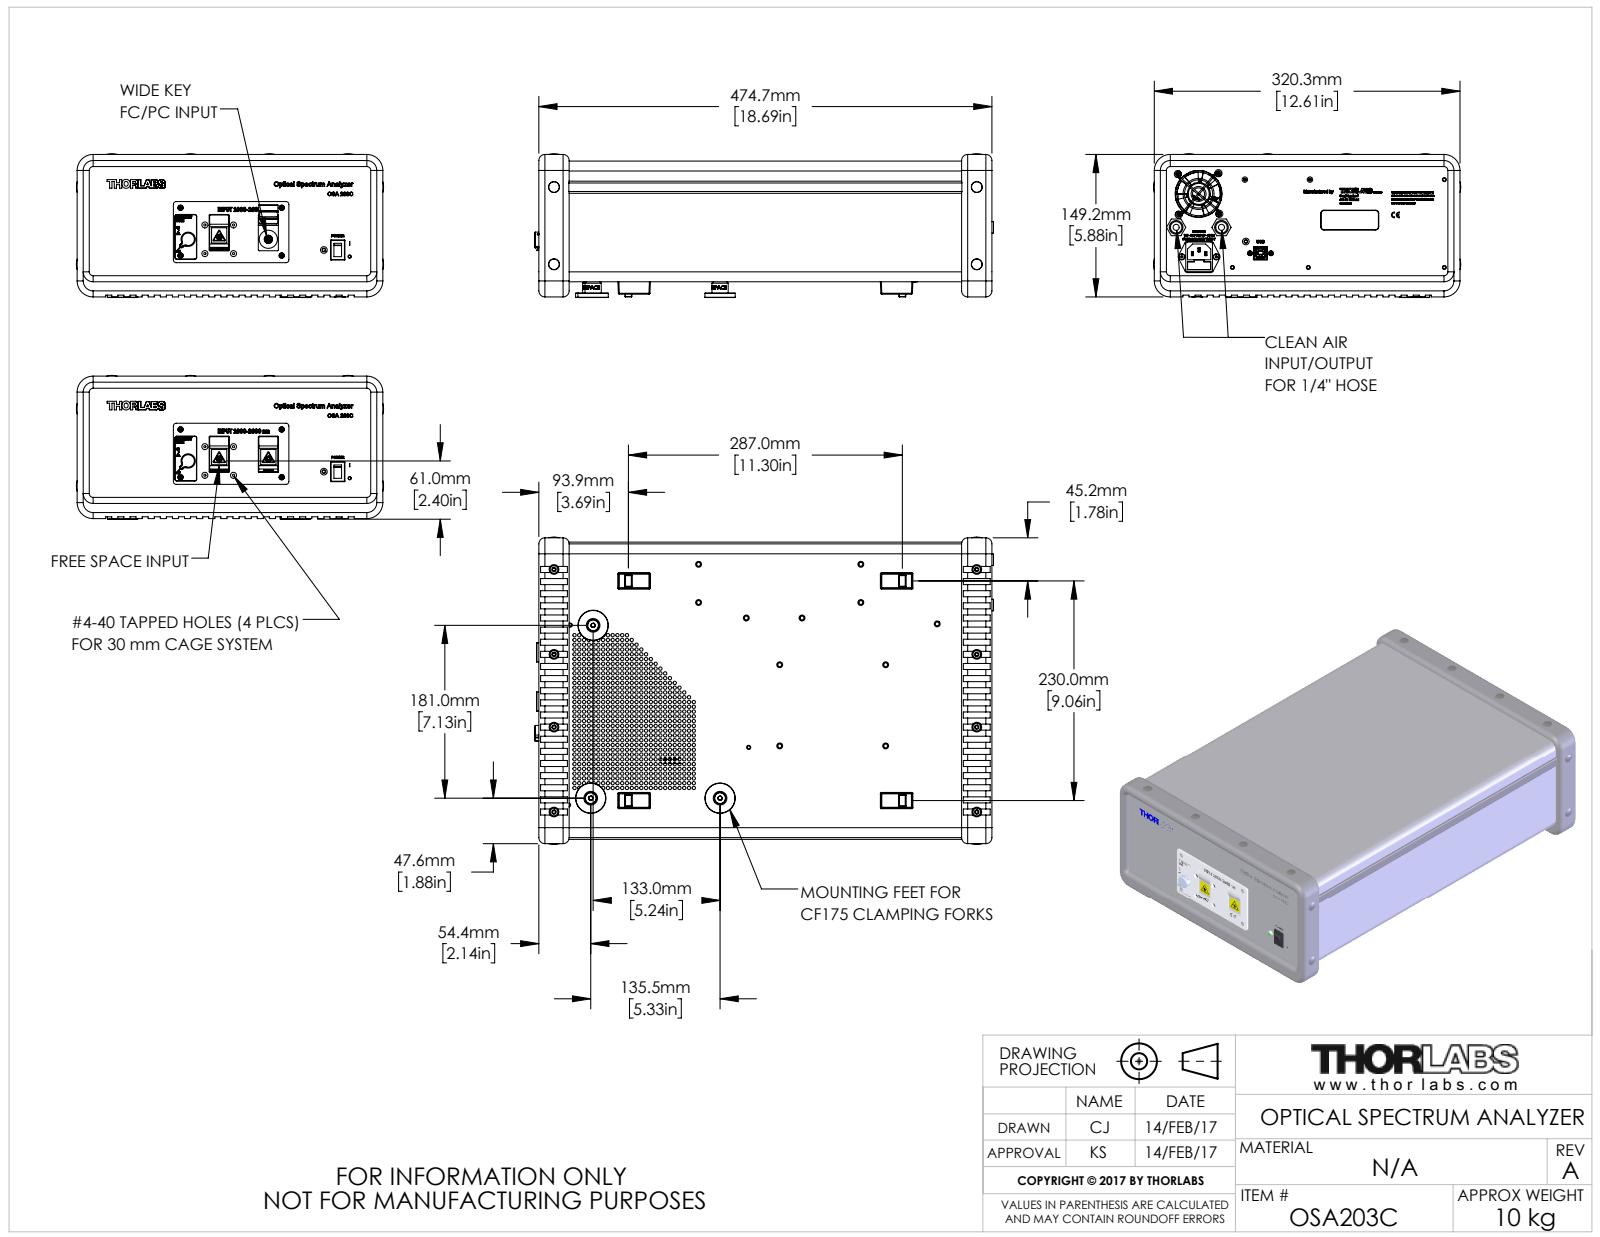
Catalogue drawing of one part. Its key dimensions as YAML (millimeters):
part_name: "MKD 110 0273_201B; EMS 110 0004; GMD 301 0001_201B; FH-M3-15-ZI_FH-M3-15-ZI-Colly (+8 more)"
step_written_by: "SolidWorks 2016 (AUTOMOTIVE_DESIGN)"
units: millimeters
bodies: {solids: 254, faces: 17519, planar: 8896, cylindrical: 3970, other: 4653}
overall_size: [480.91, 321.82, 150.61]
volume: 1899000
surface_area: 1632000
round_holes:
  - {diameter: 3.5, count: 753}
  - {diameter: 2.5, count: 49}
  - {diameter: 2.05, count: 28}
  - {diameter: 3.2, count: 26}
  - {diameter: 3.3, count: 17}
  - {diameter: 3, count: 15}
  - {diameter: 2.26, count: 13}
  - {diameter: 1.2, count: 12}
  - {diameter: 5.08, count: 12}
  - {diameter: 11.43, count: 12}
  - {diameter: 5, count: 11}
  - {diameter: 3.1, count: 9}
round_bosses_or_shafts:
  - {diameter: 3, count: 36}
  - {diameter: 4, count: 22}
  - {diameter: 5, count: 20}
  - {diameter: 6, count: 17}
  - {diameter: 7, count: 15}
  - {diameter: 2.4, count: 13}
  - {diameter: 11.05, count: 12}
  - {diameter: 5.38, count: 12}
partial_cylinders:
  - {radius: 0.5, count: 91}
  - {radius: 1, count: 56}
  - {radius: 0.27, count: 48}
  - {radius: 0.91, count: 48}
  - {radius: 1.5, count: 47}
  - {radius: 3, count: 40}
  - {radius: 0.16, count: 24}
  - {radius: 0.55, count: 24}
face_to_face_distances: [1, 125.4, 126.4, 124.4, 306.6, 461, 90.65, 34.75, 307.6, 305.6]
hole_center_spacings: [16, 25.5, 32, 105, 275.05, 5, 10, 230]
